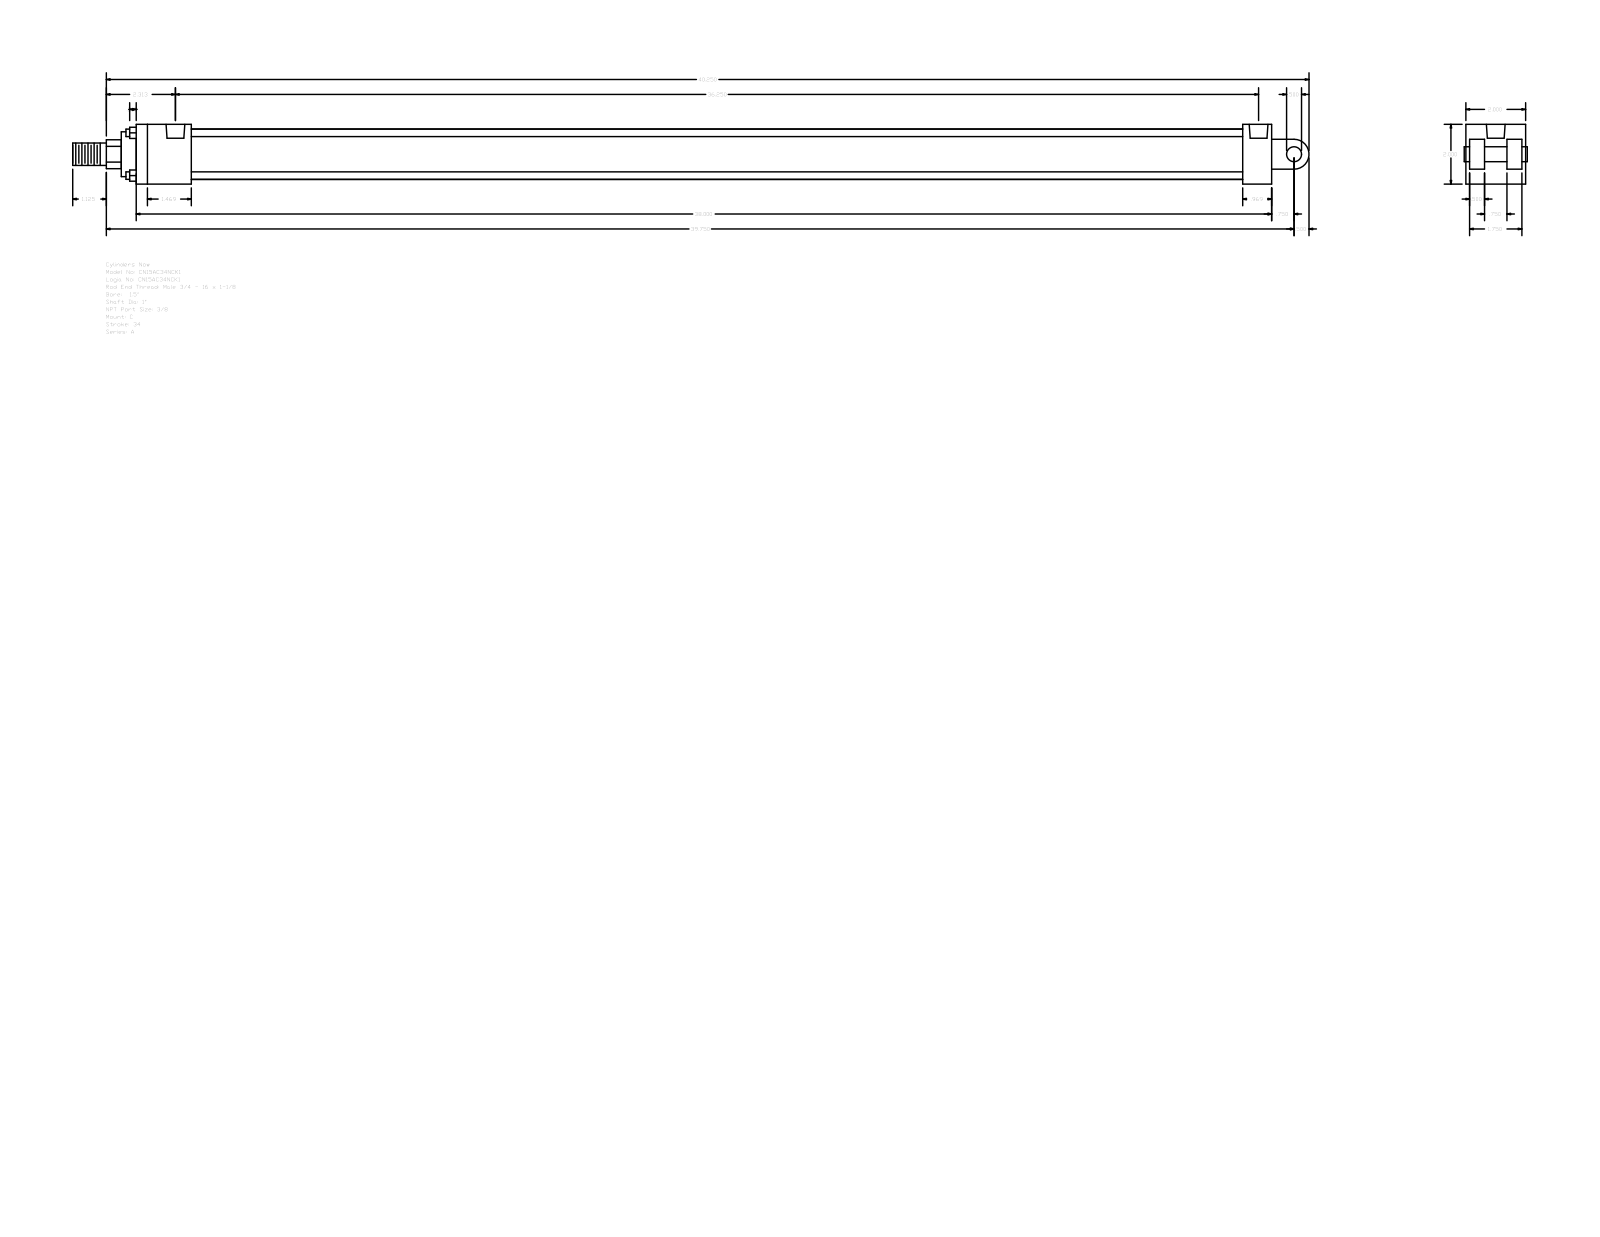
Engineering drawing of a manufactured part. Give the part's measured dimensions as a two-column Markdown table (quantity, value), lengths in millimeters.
| quantity | value |
| --- | --- |
| part name | A_C__0150_1 |
| STEP written by | GSSL Pune (CONFIG_CONTROL_DESIGN) |
| units | millimeters |
| bodies | 0 solids, 99 faces (70 planar, 29 cylindrical, 0 other) |
| overall size | 1050.92 × 50.8 × 50.8 |
| round holes (diameter × count) | 5.56 × 4, 15.93 × 2 |
| round bosses / shafts (diameter × count) | 6.35 × 4, 42.93 × 1, 38.1 × 1, 25.4 × 1, 19.05 × 1, 12.7 × 1 |
| partial cylindrical surfaces (radius × count) | 12.29 × 1, 12.7 × 1 |
| main face-to-face distances | 50.8, 12.7, 3.17, 15.87, 47.63, 34.93, 31.76, 965.2, 38.1, 940.59 |
| hole center spacings | 3.97, 912.81, 916.78, 920.75 |
